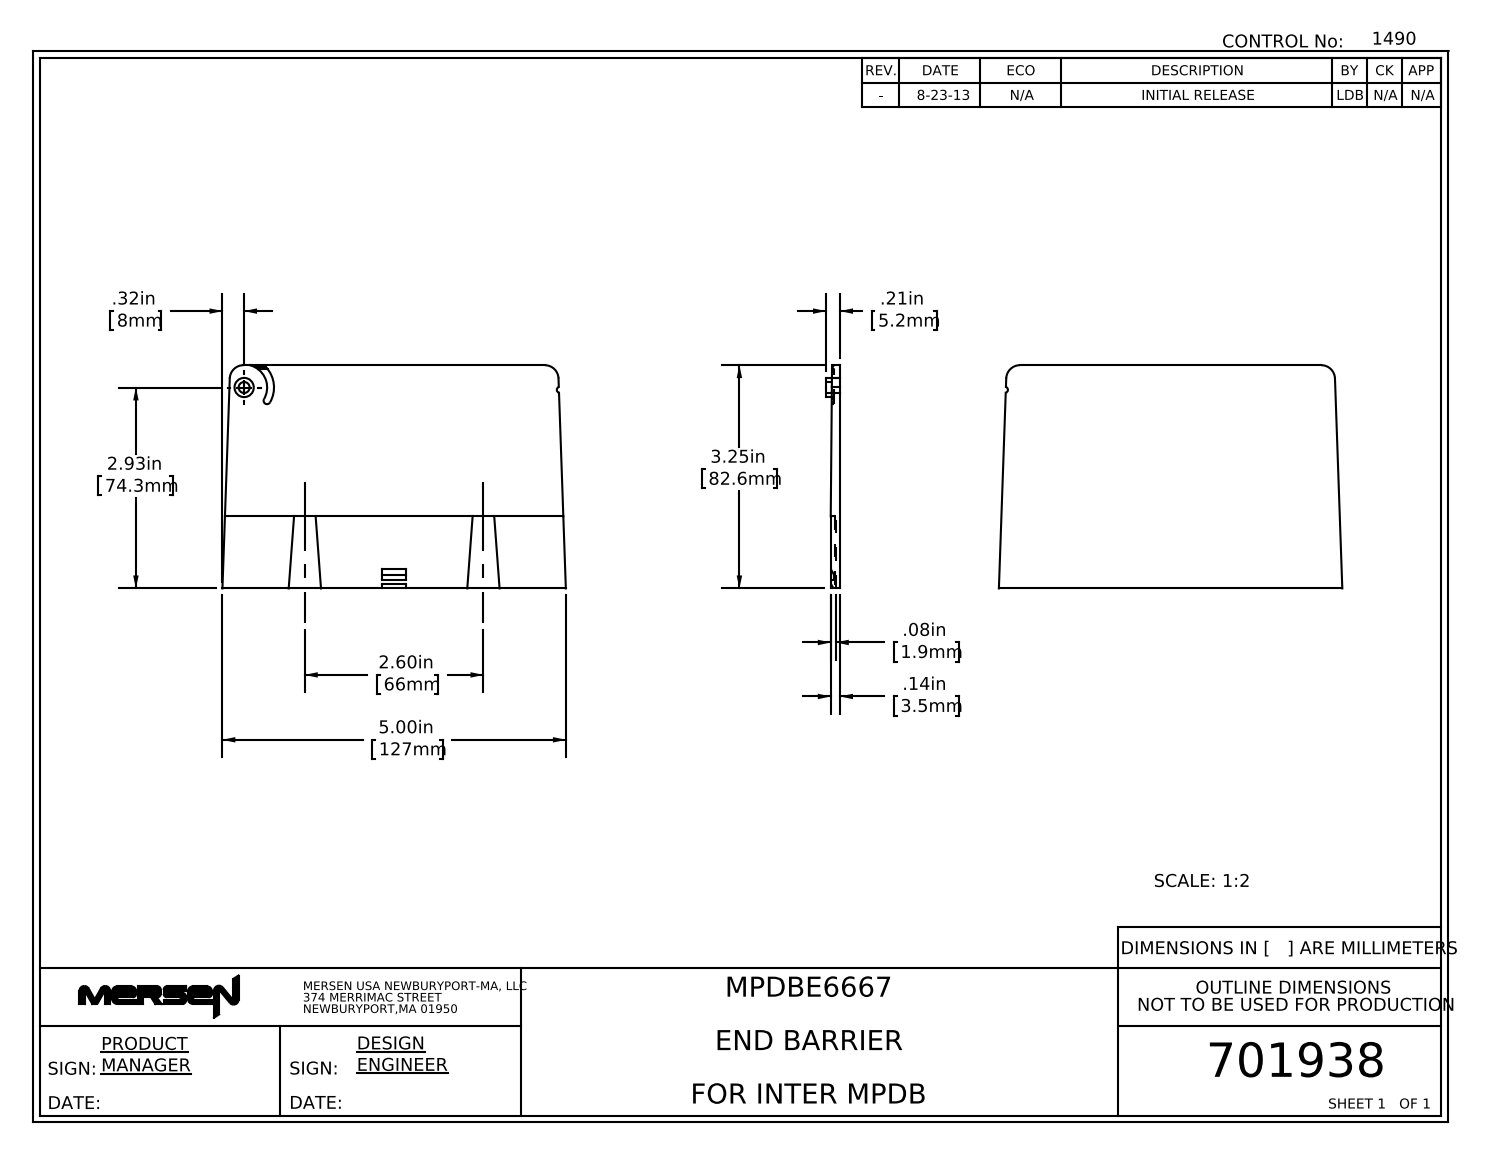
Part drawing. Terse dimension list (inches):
name: 701938rev
written by: SolidWorks 2013 (AUTOMOTIVE_DESIGN)
unit: in
bodies: 1 solid, 45 faces (31 planar, 14 cylindrical, 0 other)
size: 5 × 3.25 × 0.206
volume: 1.982 in³; area: 34.61 in²
holes: 1× ⌀0.16
bosses: 1× ⌀0.28
rounds: 4× R0.01, 2× R0.2, 1× R0.045, 1× R0.05, 1× R0.335, 1× R0.435
face distances: 0.136, 0.061, 0.075, 3.25, 1.836, 0.086, 0.025, 0.05, 0.12, 1.05
